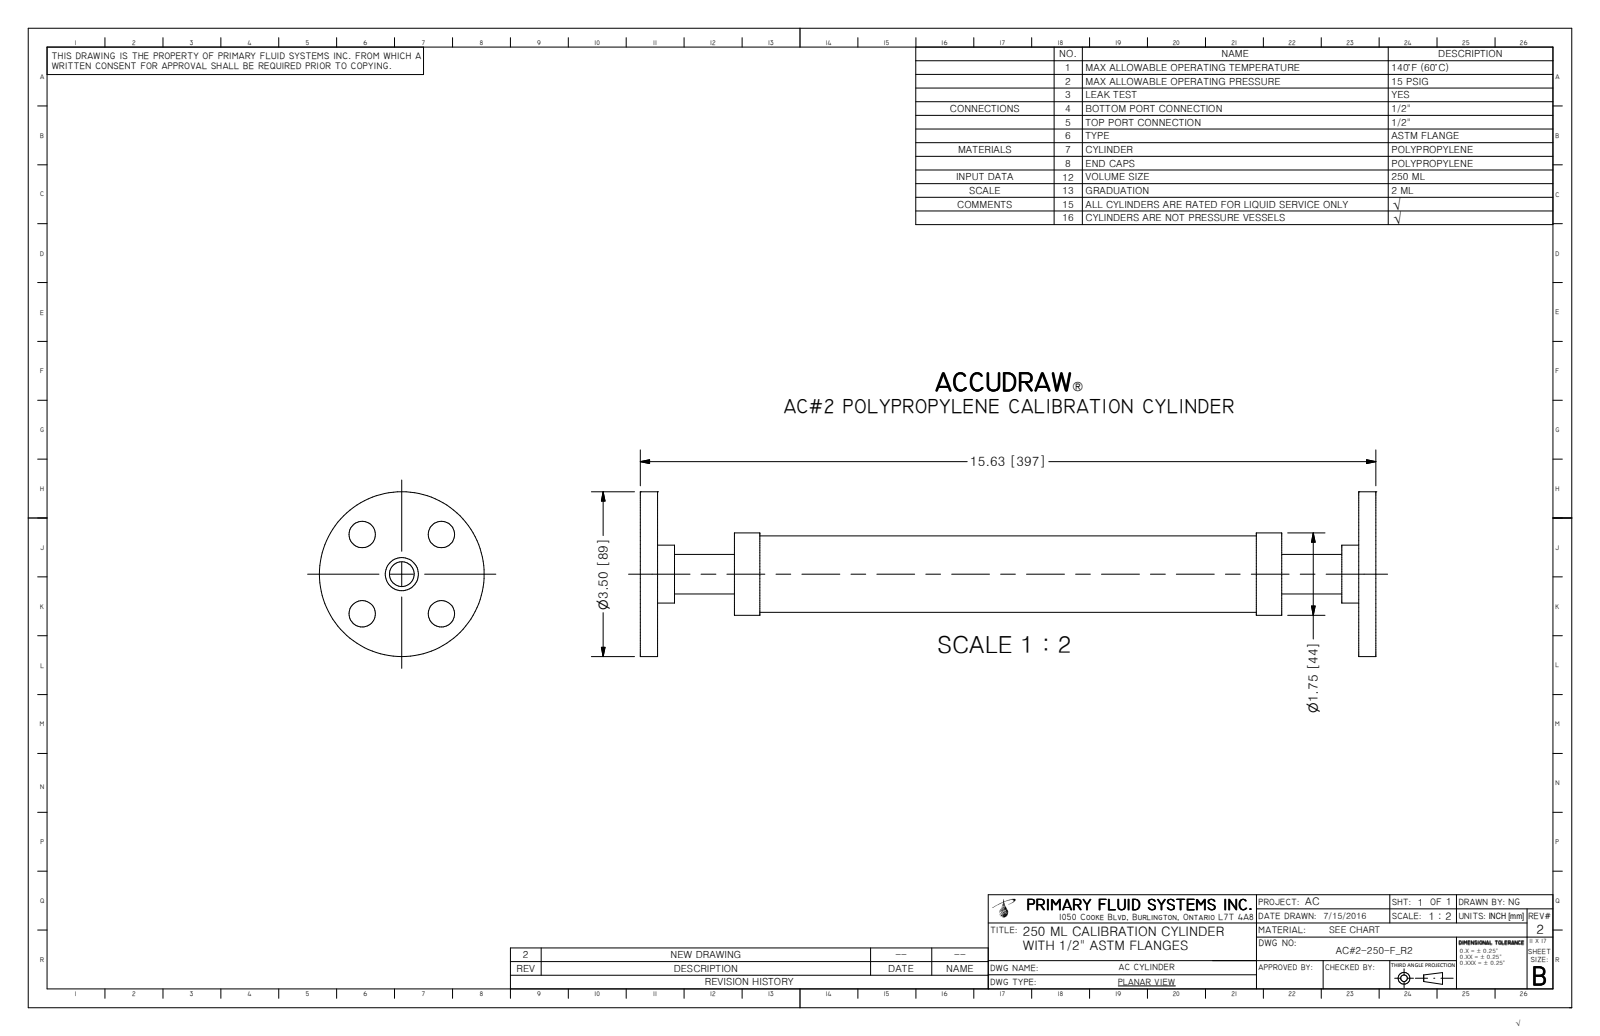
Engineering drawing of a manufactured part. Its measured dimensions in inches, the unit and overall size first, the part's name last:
Units: inches
Overall size (bounding box): 15.63 × 3.5 × 3.5
Round holes (diameter × count): ⌀0.56 ×4, ⌀0.526 ×1, ⌀0.688 ×1, ⌀0.703 ×1, ⌀0.84 ×1, ⌀1.505 ×1
Round bosses / shafts (diameter × count): ⌀3.5 ×1, ⌀1.75 ×1, ⌀1.625 ×1, ⌀1.49 ×1, ⌀1.385 ×1, ⌀1.23 ×1
Main face-to-face distances: 0.365, 15.265, 15.63, 14.9, 2, 13.63, 1.635, 13.265, 2.75, 12.88
Hole centre spacings: 1.19, 1.683, 2.38
Volume: 13.76 in³ · Surface area: 199.1 in²
Bodies: 7 solids, 52 faces (22 planar, 28 cylindrical, 2 other)
Part name (STEP PRODUCT): AC#2-250-F_R2; SA-50FLG-PP_R0; FLG-50PP_R0; PIPE-50PP-SCH80 (+3 more)
STEP written by: Autodesk Inventor 2009 (AUTOMOTIVE_DESIGN)
